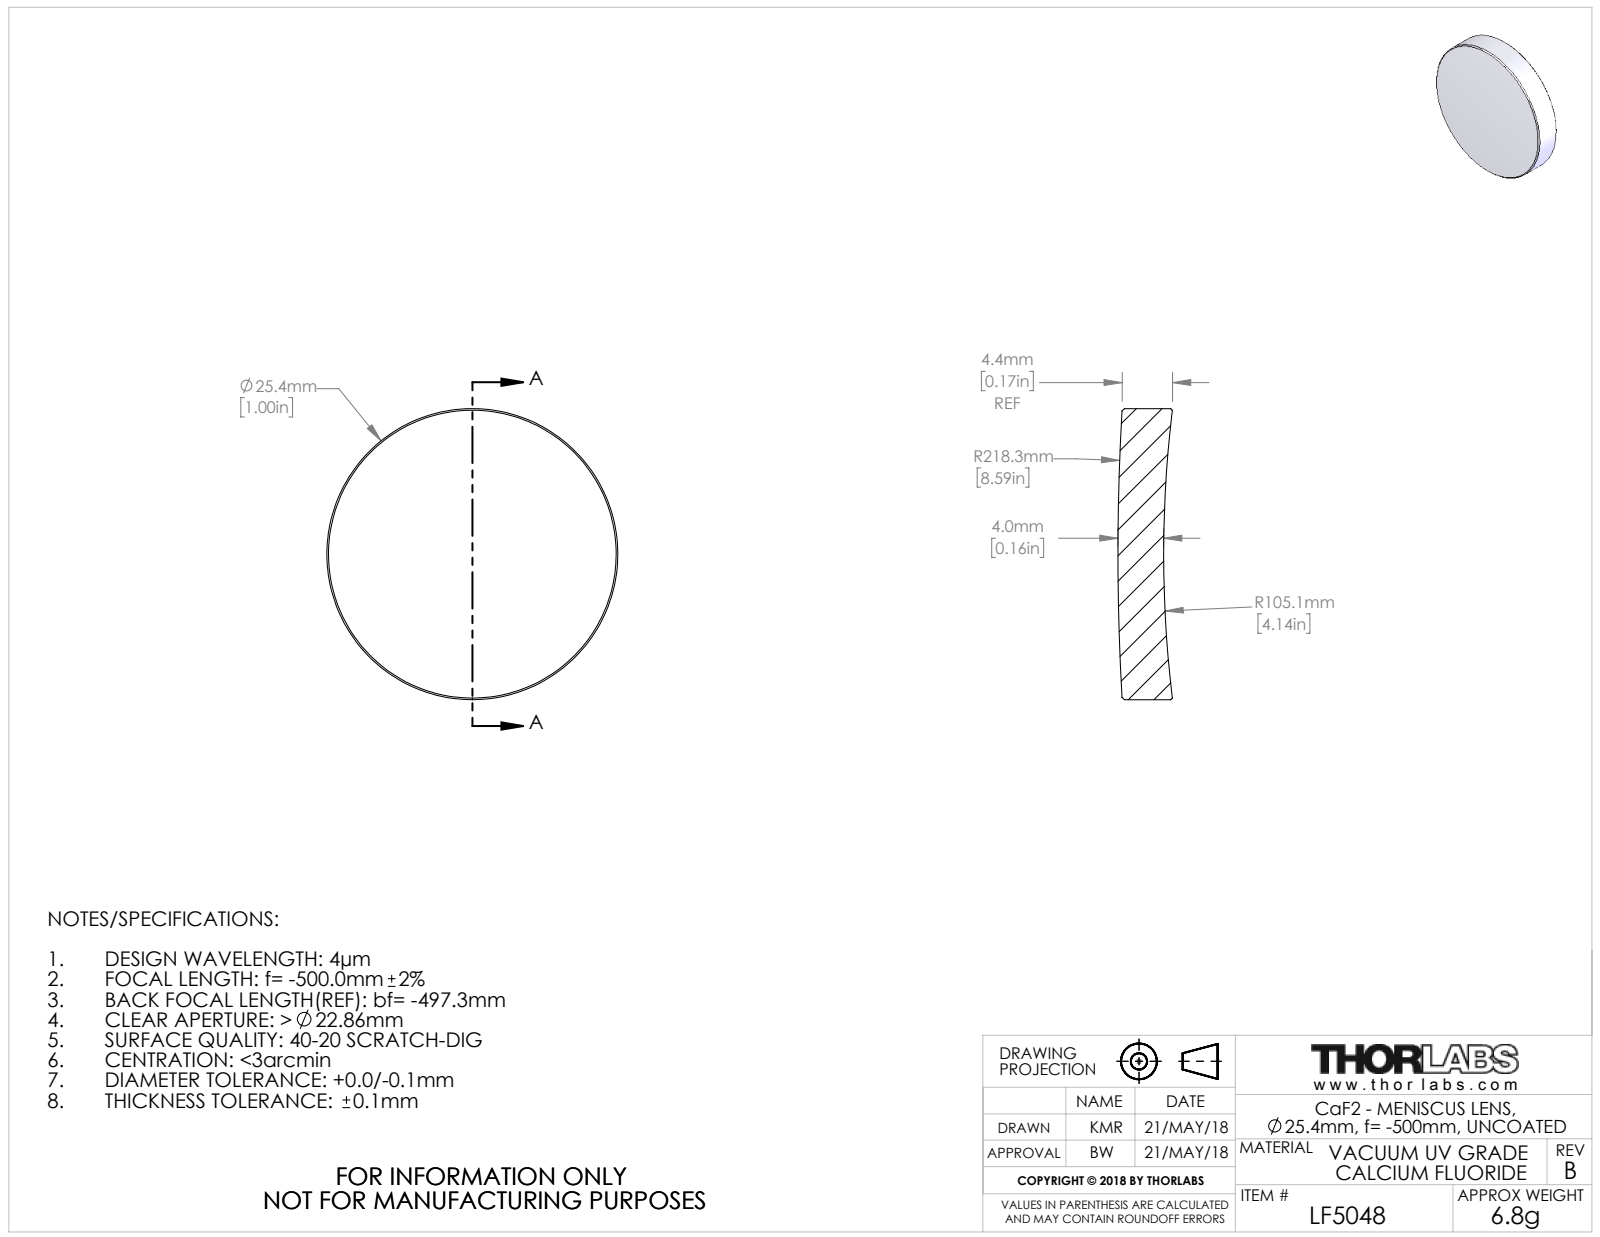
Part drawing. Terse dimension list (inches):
name: 22004-E0W
written by: SolidWorks 2016 (CONFIG_CONTROL_DESIGN)
unit: in
bodies: 1 solid, 10 faces (0 planar, 2 cylindrical, 8 other)
size: 1 × 1 × 0.187
volume: 0.13 in³; area: 2.092 in²
bosses: 1× ⌀1
